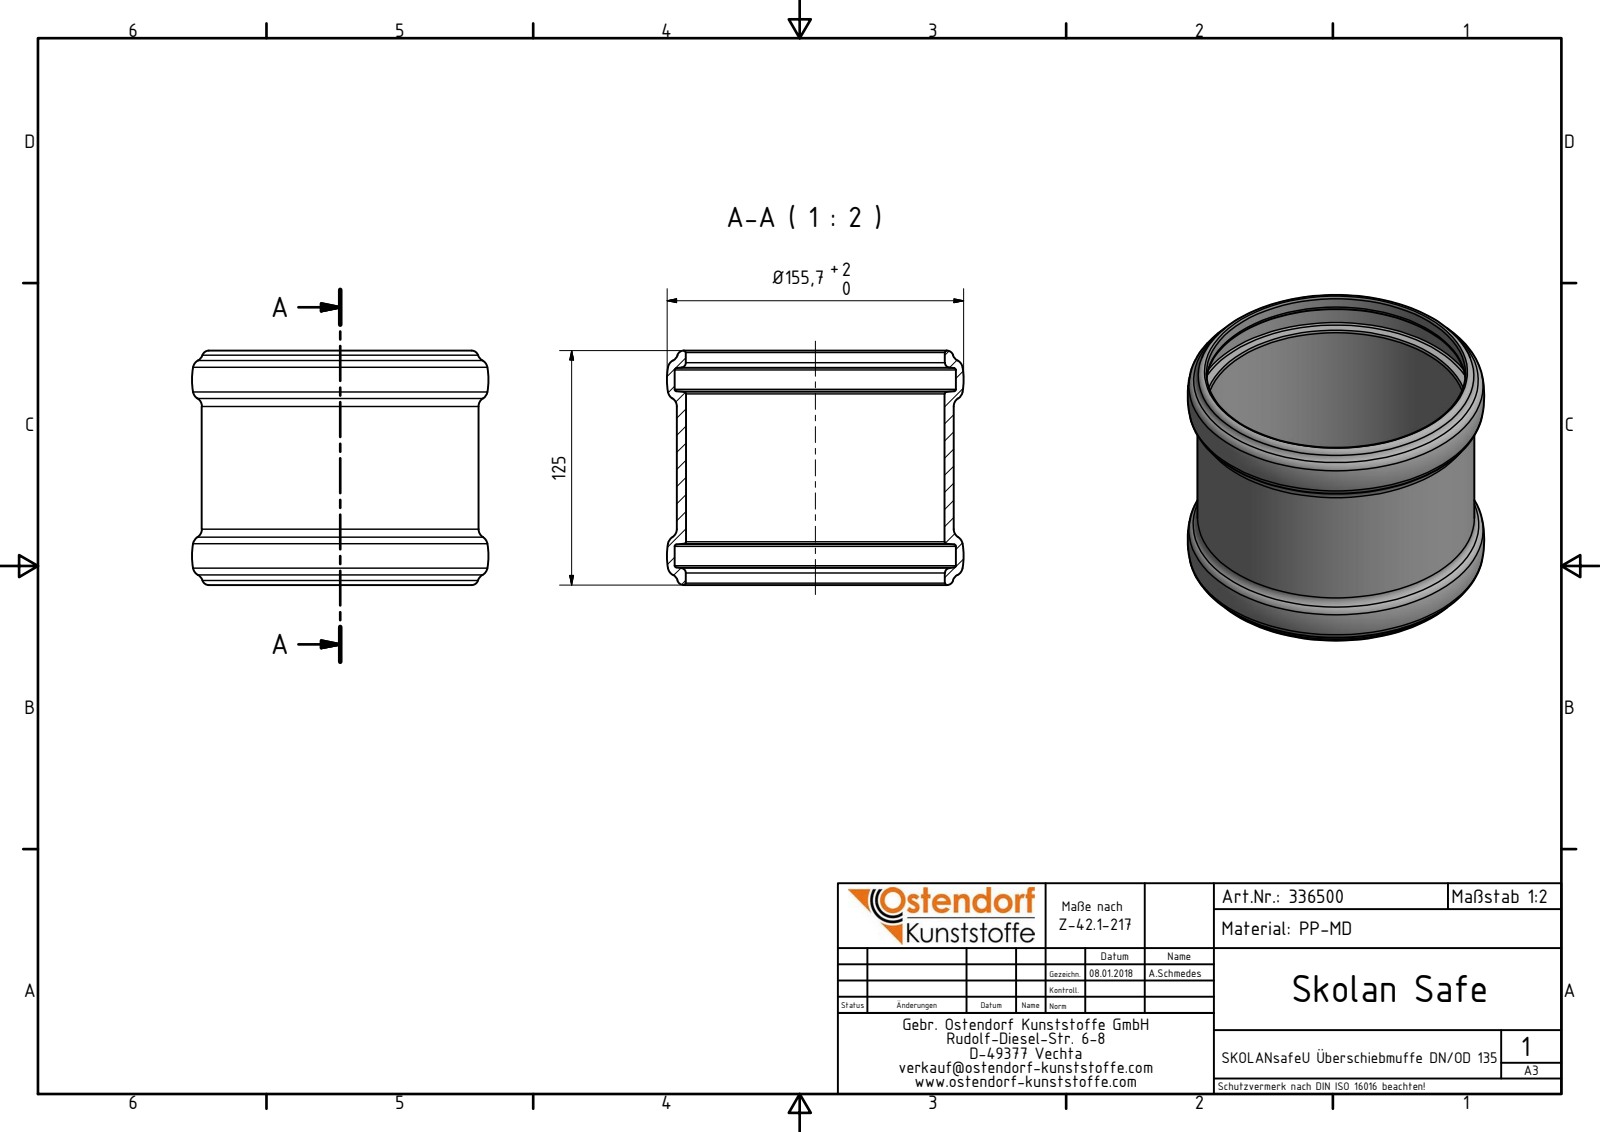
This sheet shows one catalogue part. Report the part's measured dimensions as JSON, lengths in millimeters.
{"part_name": "336500 SKOLANsafeU Überschiebmuffe DN_OD 135", "step_written_by": "Autodesk Inventor 2016 (AUTOMOTIVE_DESIGN)", "units": "millimeters", "bodies": {"solids": 1, "faces": 32, "planar": 0, "cylindrical": 6, "other": 26}, "overall_size": [155.7, 155.7, 123], "volume_mm3": 278726, "surface_area_mm2": 124246, "round_holes": [[135.8, 1], [136.1, 1], [147.7, 1]], "round_bosses_or_shafts": [[145.4, 1]]}
